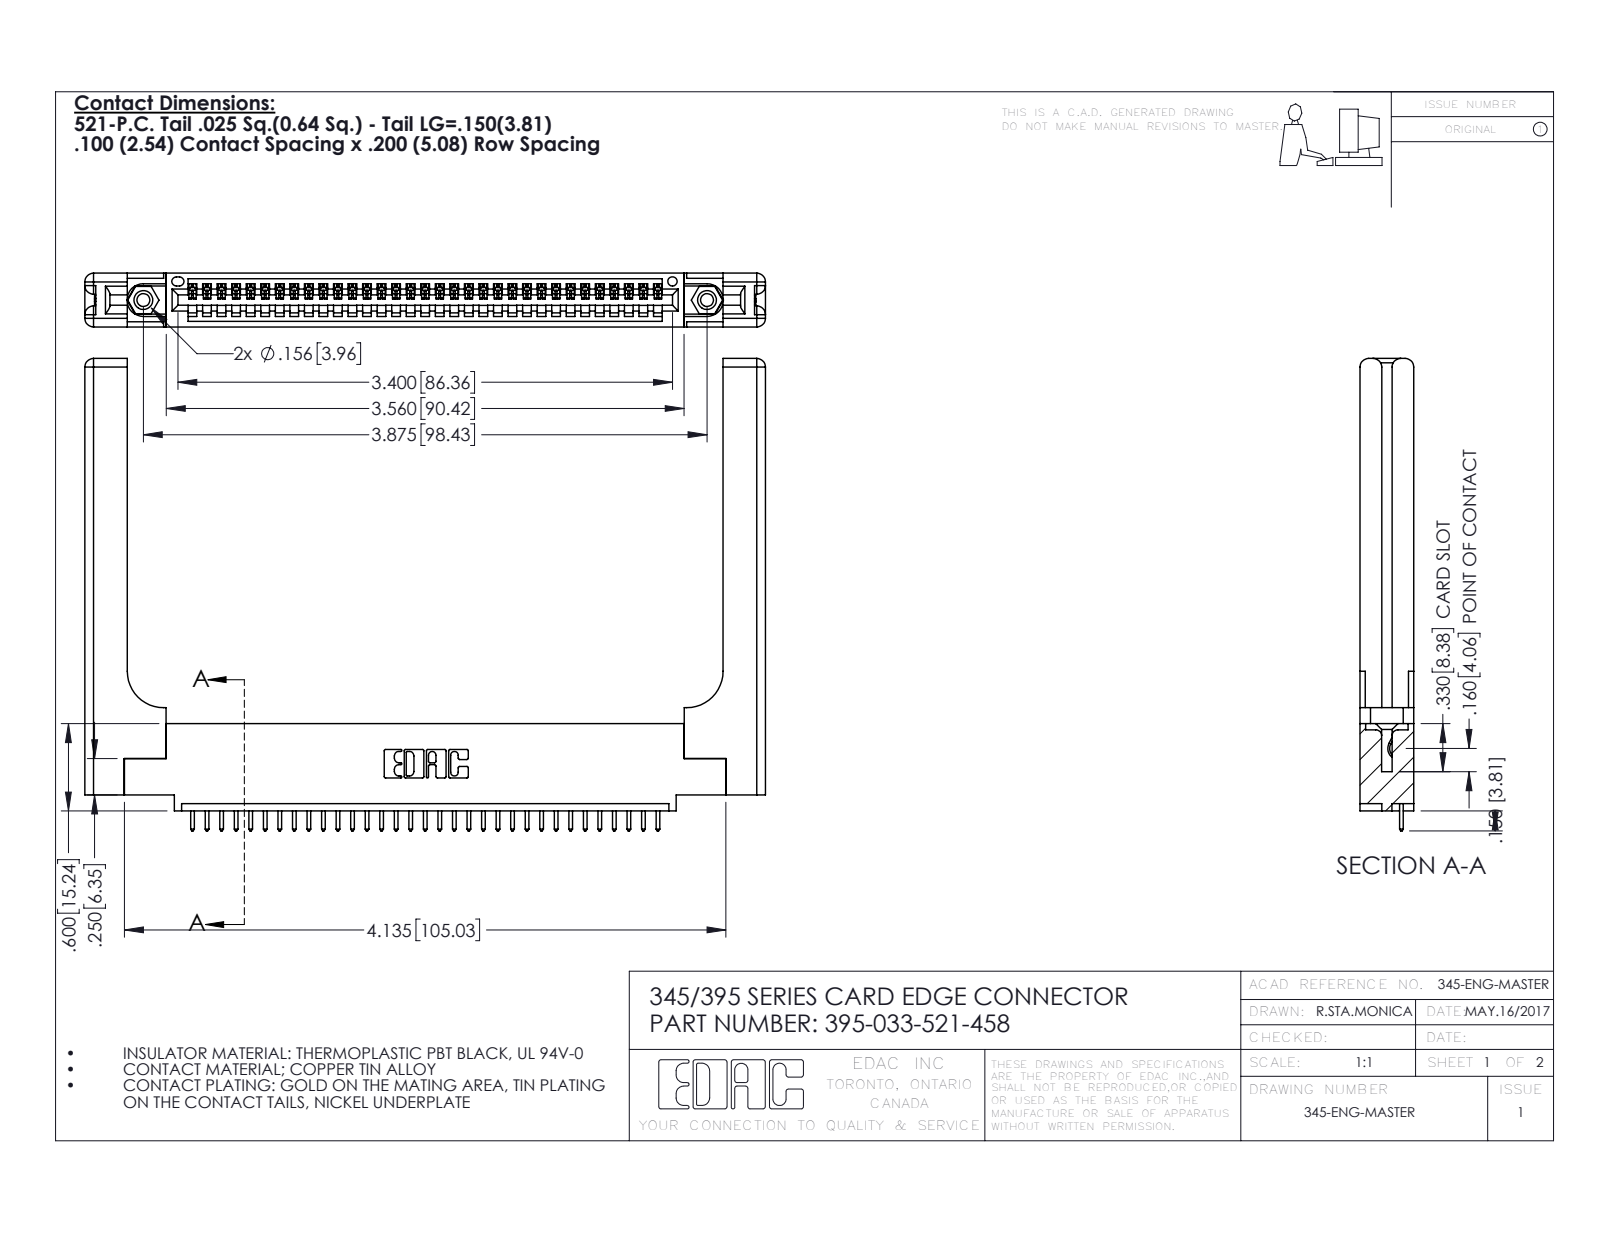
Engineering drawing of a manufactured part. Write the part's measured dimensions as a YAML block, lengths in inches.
part_name: "345-250-001_345-250-001-102; 345 Part_0.110 Offset - 0.156 Dia-TH; 395-033-521-458; 345-292-001_345-293-121 (+1 more)"
step_written_by: "SolidWorks 2016 (CONFIG_CONTROL_DESIGN)"
units: inches
bodies: {solids: 38, faces: 2300, planar: 1552, cylindrical: 688, other: 60}
overall_size: [4.679, 3.247, 0.37]
volume: 1.193
surface_area: 30.35
round_holes:
  - {diameter: 0.089, count: 2}
  - {diameter: 0.125, count: 2}
  - {diameter: 0.156, count: 2}
  - {diameter: 0.064, count: 1}
round_bosses_or_shafts:
  - {diameter: 0.155, count: 2}
partial_cylinders:
  - {radius: 0.006, count: 66}
  - {radius: 0.01, count: 66}
  - {radius: 0.01, count: 22}
  - {radius: 0.06, count: 16}
  - {radius: 0.007, count: 6}
  - {radius: 0.031, count: 6}
  - {radius: 0.026, count: 3}
  - {radius: 0.03, count: 2}
face_to_face_distances: [0.37, 0.072, 0.298, 0.098, 0.272, 0.025, 0.2, 0.148, 0.15, 0.077]
hole_center_spacings: [0.27, 3.64, 3.875]
